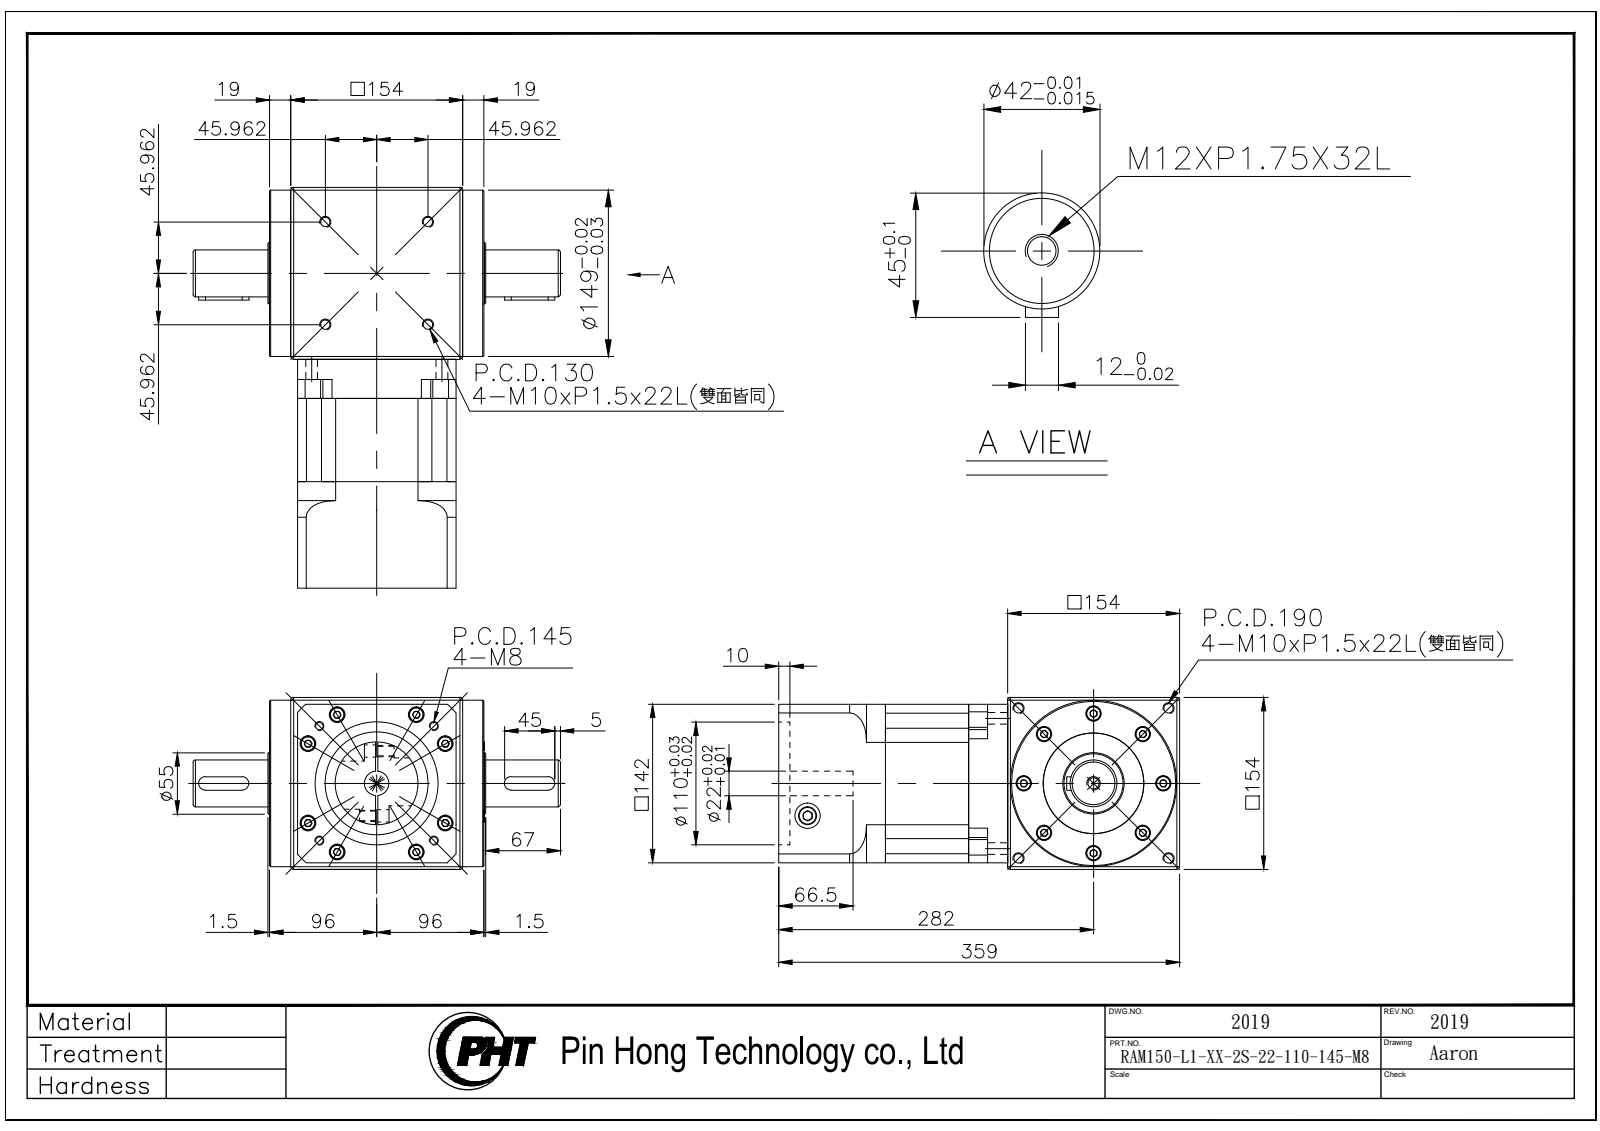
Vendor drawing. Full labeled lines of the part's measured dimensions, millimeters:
Part name (STEP PRODUCT): RAM150-L1-XX-2S-22-110-145-M8_2019
STEP written by: SolidWorks 2016 (AUTOMOTIVE_DESIGN)
Units: millimetres
Bodies: 6 solids, 899 faces (435 planar, 300 cylindrical, 164 other)
Overall size (bounding box): 359 × 329 × 154
Volume: 8 009 000 mm³ · Surface area: 528 584 mm²
Round holes (diameter × count): ⌀8.5 ×12, ⌀9 ×8, ⌀11 ×8, ⌀14 ×8, ⌀17.5 ×8, ⌀6.8 ×4, ⌀10.5 ×4, ⌀22.5 ×2, ⌀4.08 ×1, ⌀10.2 ×1, ⌀22 ×1, ⌀92 ×1
Round bosses / shafts (diameter × count): ⌀16 ×12, ⌀13 ×8, ⌀149 ×1, ⌀130 ×1, ⌀90 ×1, ⌀74 ×1, ⌀55 ×1, ⌀42 ×1
Partial cylindrical surfaces — rounded edges, fillets, slot ends (radius × count): R6 ×4, R10 ×4, R80 ×1, R95 ×1, R107.4 ×1
Main face-to-face distances: 6, 148, 154, 142, 74.5, 35, 109.5, 263.5, 189, 167
Hole centre spacings: 71, 18.72, 18.79, 23.06, 47.83, 67.34, 82.93, 87.37
